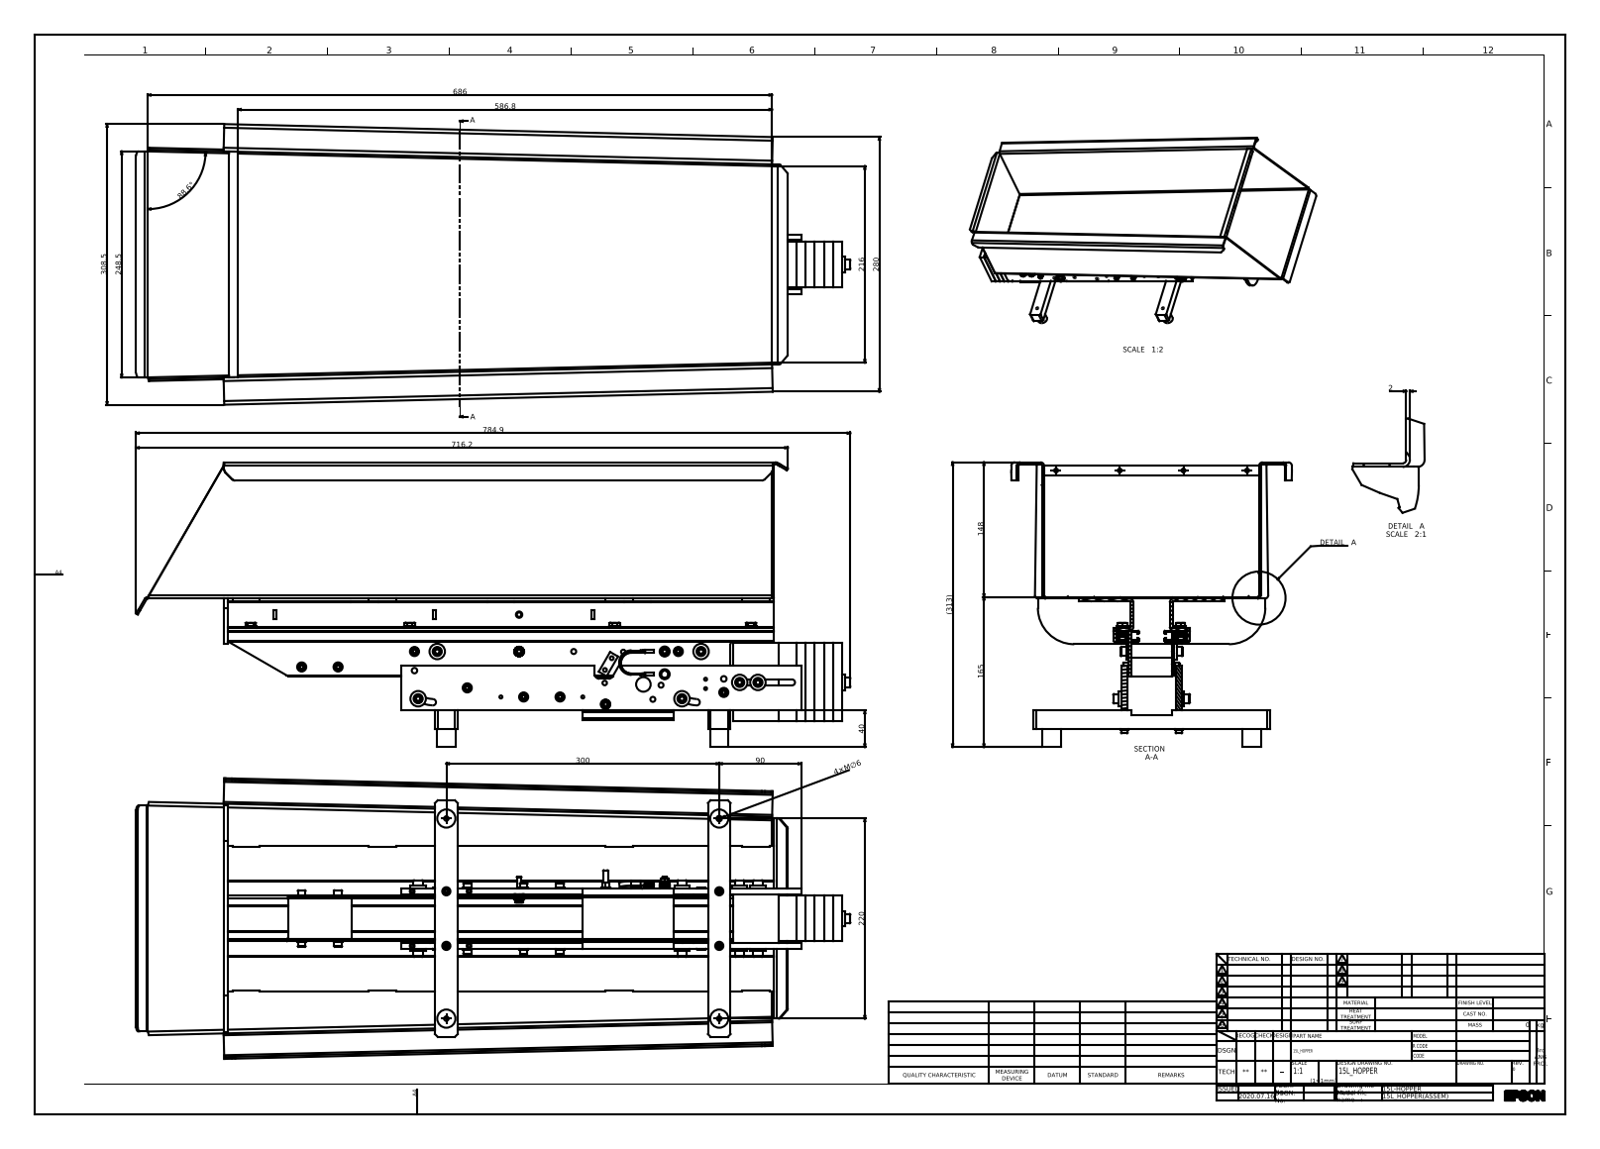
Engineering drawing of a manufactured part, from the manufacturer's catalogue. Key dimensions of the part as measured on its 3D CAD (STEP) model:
Part name (STEP PRODUCT): IMPORT_E134_1; IMPORT_E179_1; IMPORT_E137_1; CONE_3-143322_1 (+8 more)
STEP written by: SolidWorks 2013 (AUTOMOTIVE_DESIGN)
Units: millimetres
Bodies: 123 solids, 5589 faces (2821 planar, 1929 cylindrical, 839 other)
Overall size (bounding box): 784.89 × 313 × 308.5
Volume: 2 751 000 mm³ · Surface area: 1 815 000 mm²
Round holes (diameter × count): ⌀4.2 ×16, ⌀5.5 ×15, ⌀5 ×13, ⌀3.3 ×12, ⌀7 ×9, ⌀4 ×8, ⌀6.4 ×8, ⌀5.3 ×6, ⌀2.5 ×4, ⌀4.3 ×4, ⌀4.5 ×4, ⌀4.13 ×3
Round bosses / shafts (diameter × count): ⌀10 ×18, ⌀6 ×12, ⌀12 ×8, ⌀8.88 ×8, ⌀8.5 ×8, ⌀17 ×7, ⌀20 ×4, ⌀10.2 ×4
Partial cylindrical surfaces — rounded edges, fillets, slot ends (radius × count): R1 ×28, R2 ×14, R4 ×13, R5 ×12, R0.7 ×4, R2.75 ×4, R3 ×4, R3.5 ×4
Main face-to-face distances: 2, 3, 5, 47, 10, 45, 49, 50, 7, 6
Hole centre spacings: 140, 40.05, 64, 73.78, 153.94, 60, 100.02, 117.66
